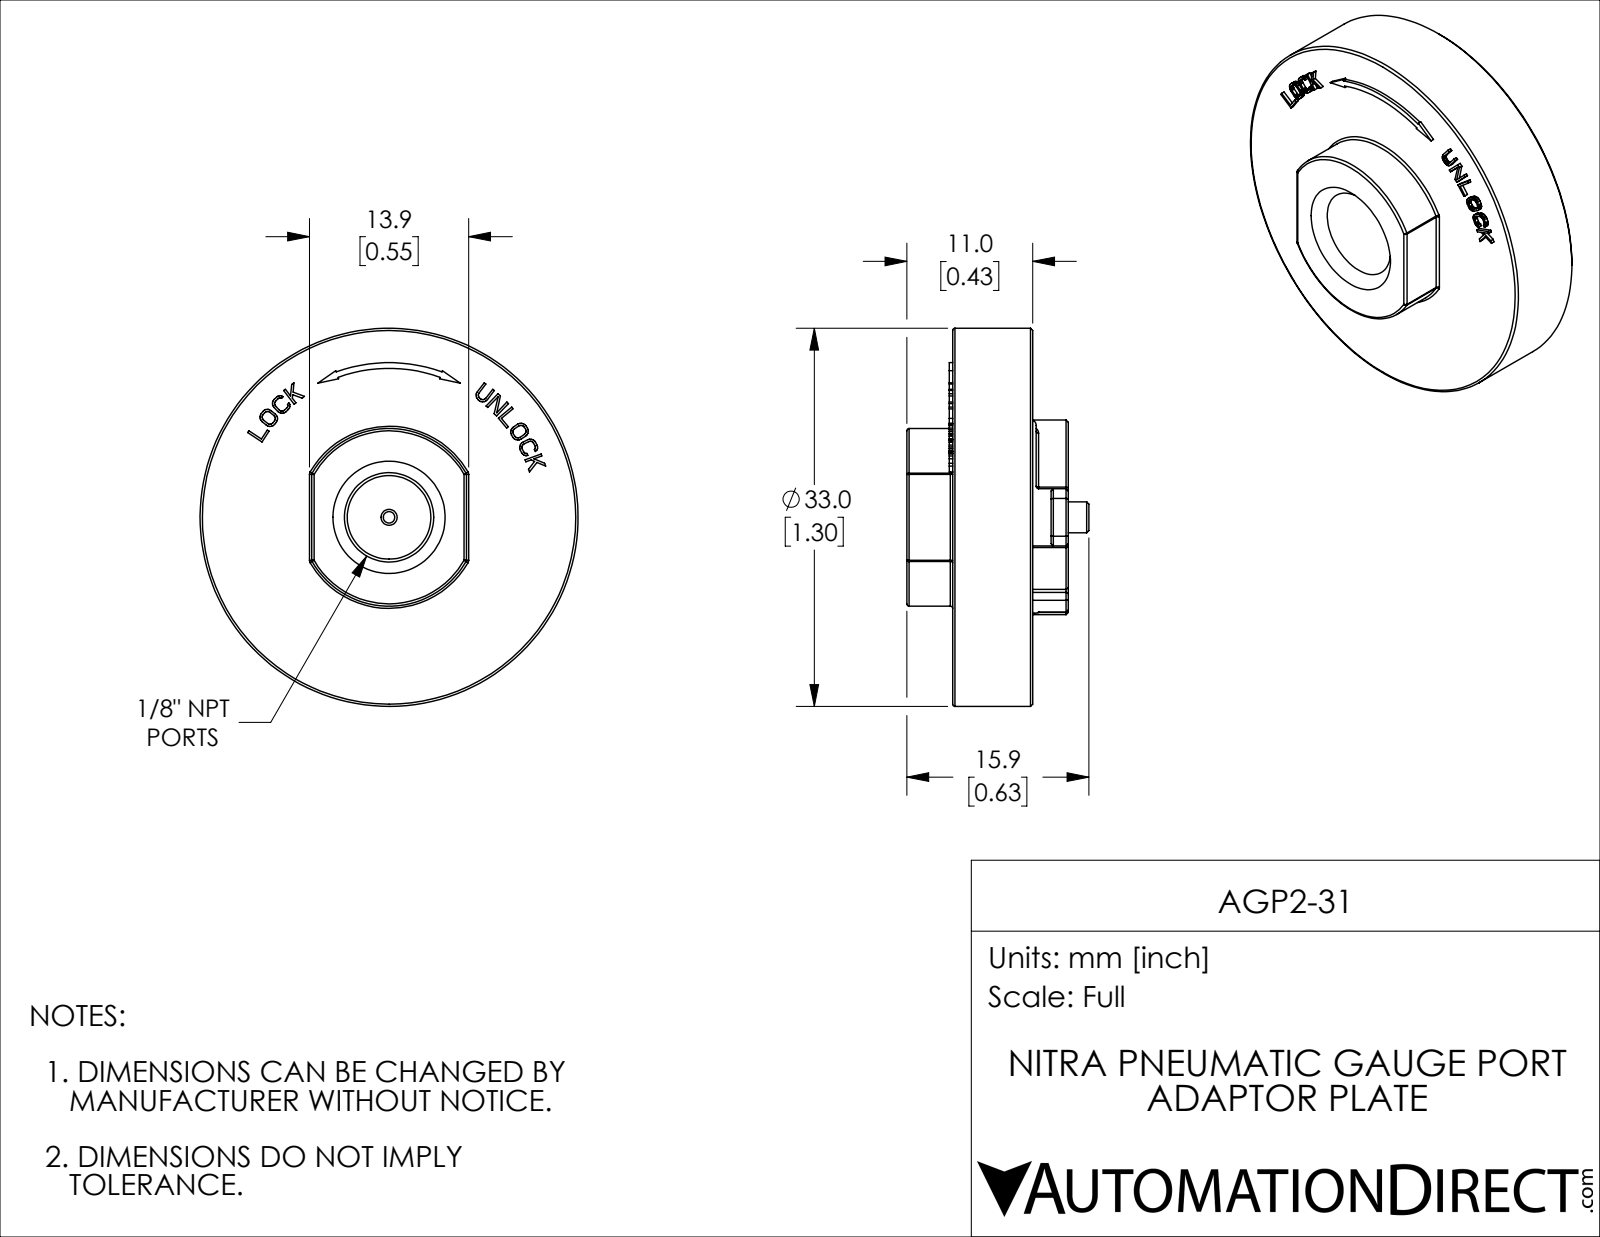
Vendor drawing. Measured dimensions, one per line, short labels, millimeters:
name: AGP2-31
written by: SolidWorks 2019 (CONFIG_CONTROL_DESIGN)
unit: mm
bodies: 1 solid, 498 faces (303 planar, 90 cylindrical, 105 other)
size: 33 × 33 × 15.9
volume: 5 390 mm³; area: 3 930 mm²
holes: 1× ⌀1
bosses: 1× ⌀33, 1× ⌀2.7
rounds: 39× R0.2, 4× R1, 4× R1.5, 1× R7.7, 1× R8.5, 1× R9.5, 1× R11.5, 1× R13
face distances: 2, 5, 7, 10.1, 8.1, 3.1, 6, 4, 11, 14.1
